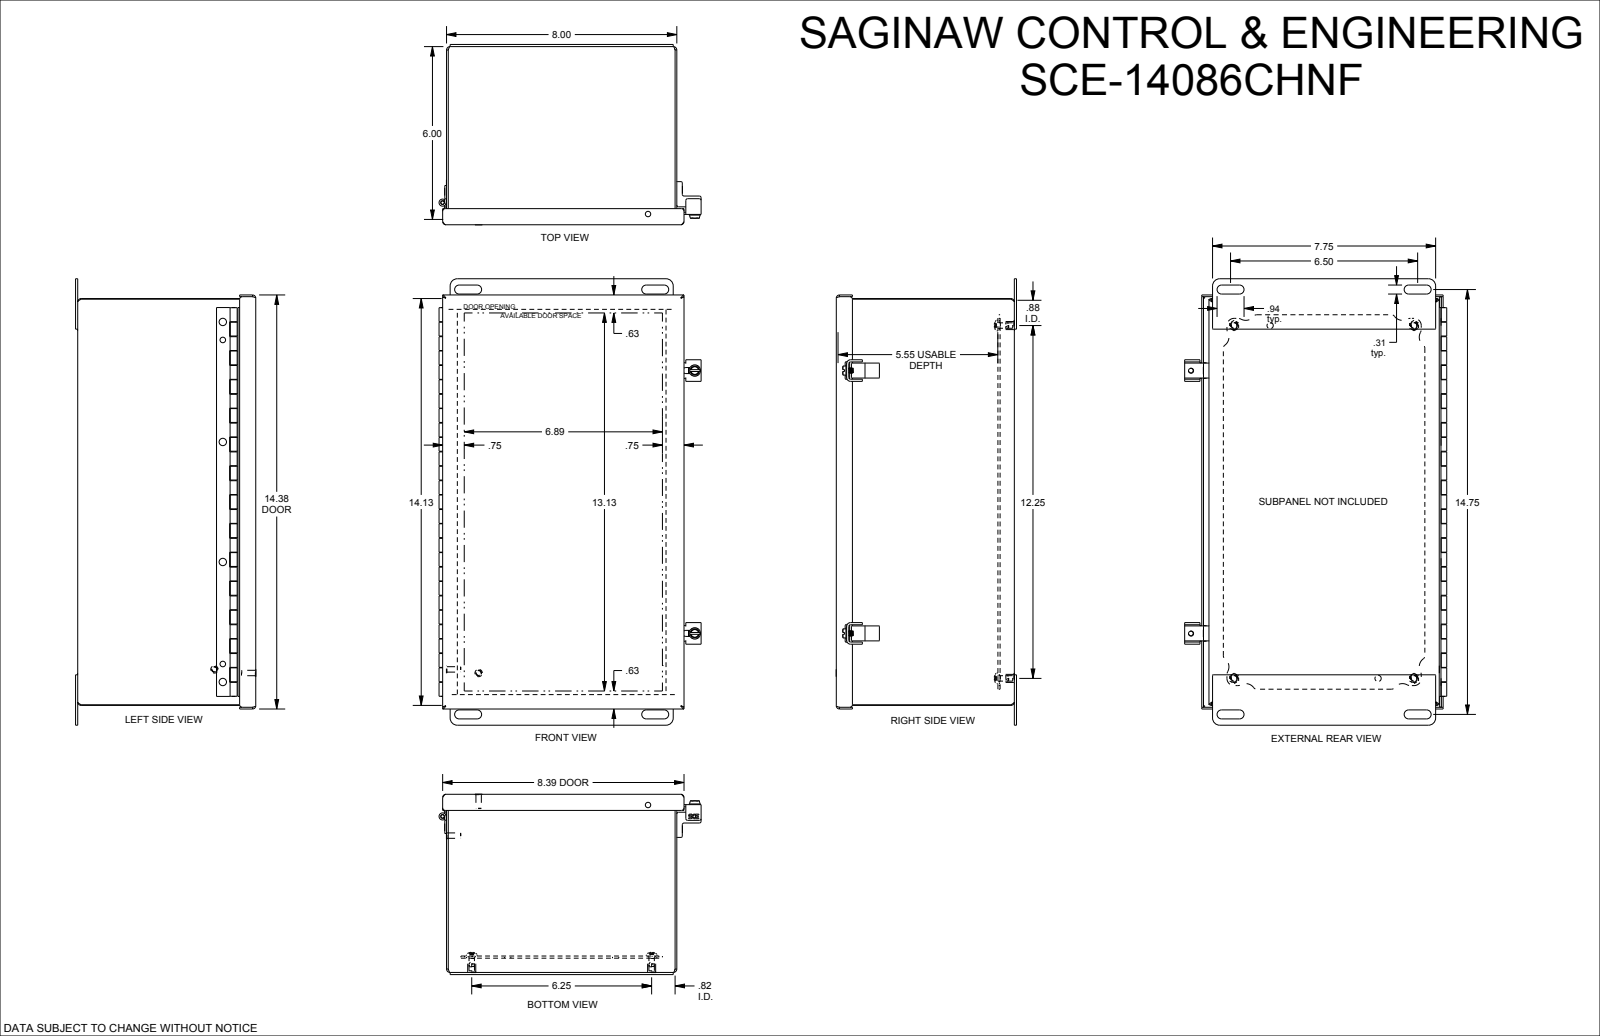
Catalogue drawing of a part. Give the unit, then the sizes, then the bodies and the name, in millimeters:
Units: millimetres
Overall size (bounding box): 393.7 × 231.2 × 159.1
Round holes (diameter × count): ⌀4.9 ×8, ⌀4.8 ×4, ⌀6.4 ×4, ⌀7.1 ×4, ⌀4 ×2, ⌀5.5 ×2, ⌀6.8 ×2, ⌀3.2 ×1, ⌀4.7 ×1
Round bosses / shafts (diameter × count): ⌀4.8 ×12, ⌀6.5 ×8, ⌀9.5 ×4, ⌀7.1 ×4, ⌀10.1 ×2, ⌀4.8 ×2, ⌀6.2 ×1, ⌀3.1 ×1
Partial cylindrical surfaces — rounded edges, fillets, slot ends (radius × count): R0.3 ×46, R1.5 ×33, R6.4 ×16, R1.3 ×8, R3.2 ×8, R4 ×8, R8.7 ×8, R0.7 ×6
Main face-to-face distances: 1.5, 155.6, 201.7, 157.1, 154.1, 1.9, 357.3, 13, 11, 14.5
Hole centre spacings: 311.1, 349.3, 27.1, 31.8, 55, 55, 63, 90
Volume: 742 500 mm³ · Surface area: 916 100 mm²
Bodies: 33 solids, 1058 faces (530 planar, 325 cylindrical, 203 other)
Part name (STEP PRODUCT): SCE-14086CHNF
STEP written by: SolidWorks 2019 (AUTOMOTIVE_DESIGN)
